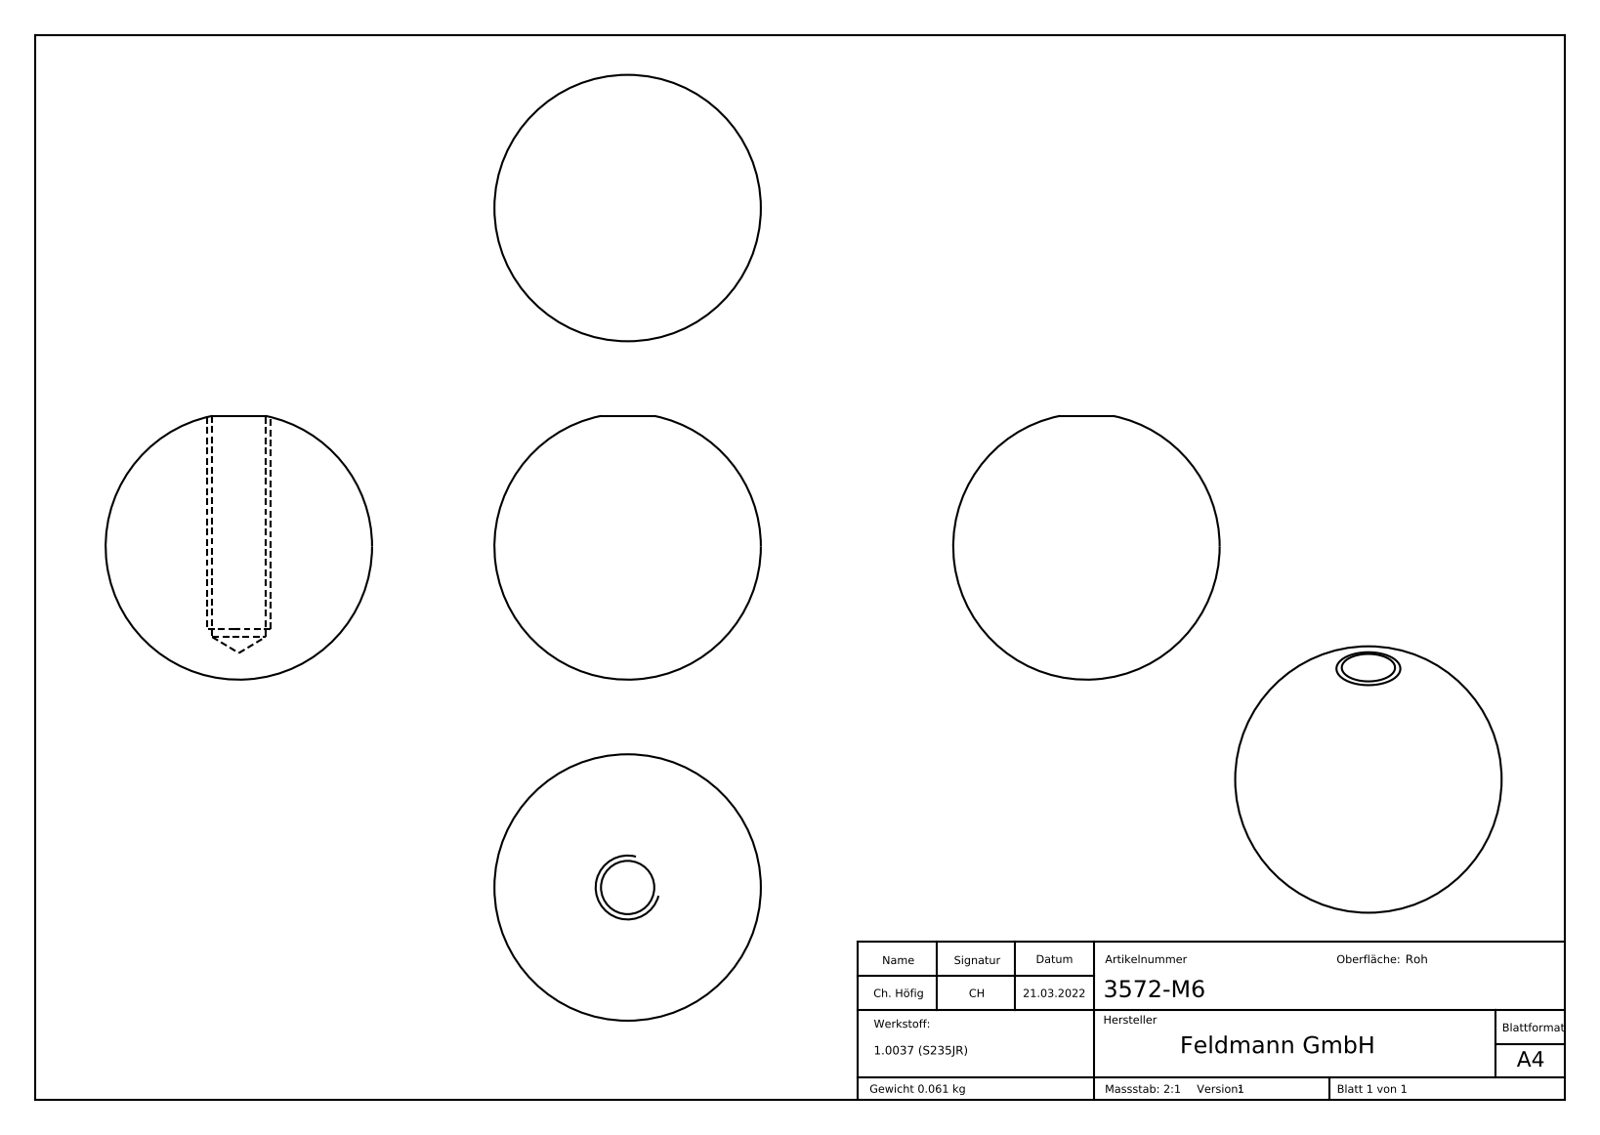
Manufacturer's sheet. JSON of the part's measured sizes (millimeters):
{"part_name": "3572-M6", "step_written_by": "SolidWorks 2018 (CONFIG_CONTROL_DESIGN)", "units": "millimeters", "bodies": {"solids": 1, "faces": 3, "planar": 0, "cylindrical": 1, "other": 2}, "overall_size": [25, 25, 24.75], "volume_mm3": 7762, "surface_area_mm2": 2292, "round_holes": [[5, 1]]}
